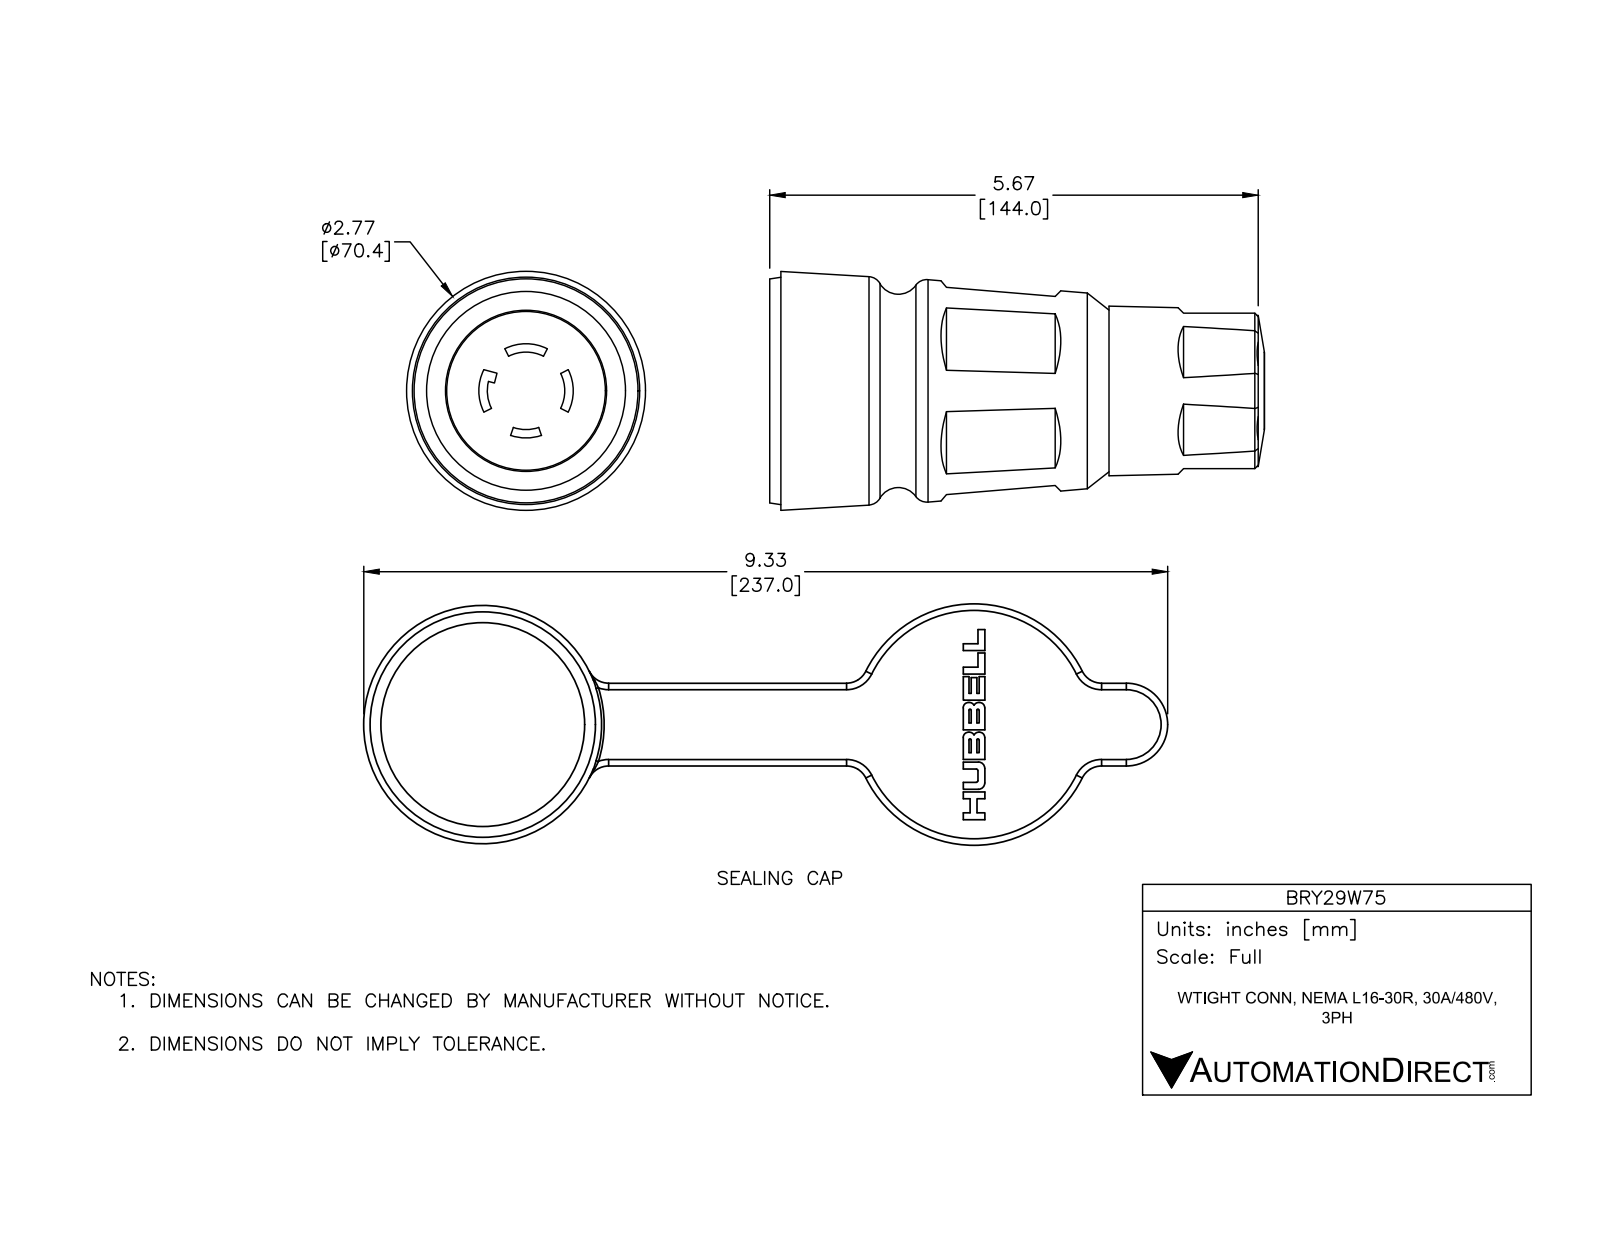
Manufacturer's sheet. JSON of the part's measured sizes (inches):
{"part_name": "BRY29W76; BRY29W-CAP; BRY29W76-CONNECTOR", "step_written_by": "SolidWorks 2016 (AUTOMOTIVE_DESIGN)", "units": "inches", "bodies": {"solids": 5, "faces": 183, "planar": 76, "cylindrical": 51, "other": 56}, "overall_size": [9.291, 5.741, 2.785], "volume_in3": 21.54, "surface_area_in2": 140.7, "round_holes": [[0.807, 1], [1.752, 1], [1.87, 1], [2.008, 1], [2.283, 1], [2.307, 1]], "round_bosses_or_shafts": [[2.785, 1], [2.622, 1], [2.421, 1], [2.299, 1], [1.843, 1], [1.555, 1]], "partial_cylinders_radius": [[0.069, 4], [0.236, 4], [0.157, 2], [0.449, 1], [0.482, 1], [0.547, 1]], "face_to_face_distances": [0.146, 0.468, 0.613, 1.354, 0.887, 0.741, 0.743, 0.276, 0.13, 0.611], "hole_center_spacings": [5.622]}
